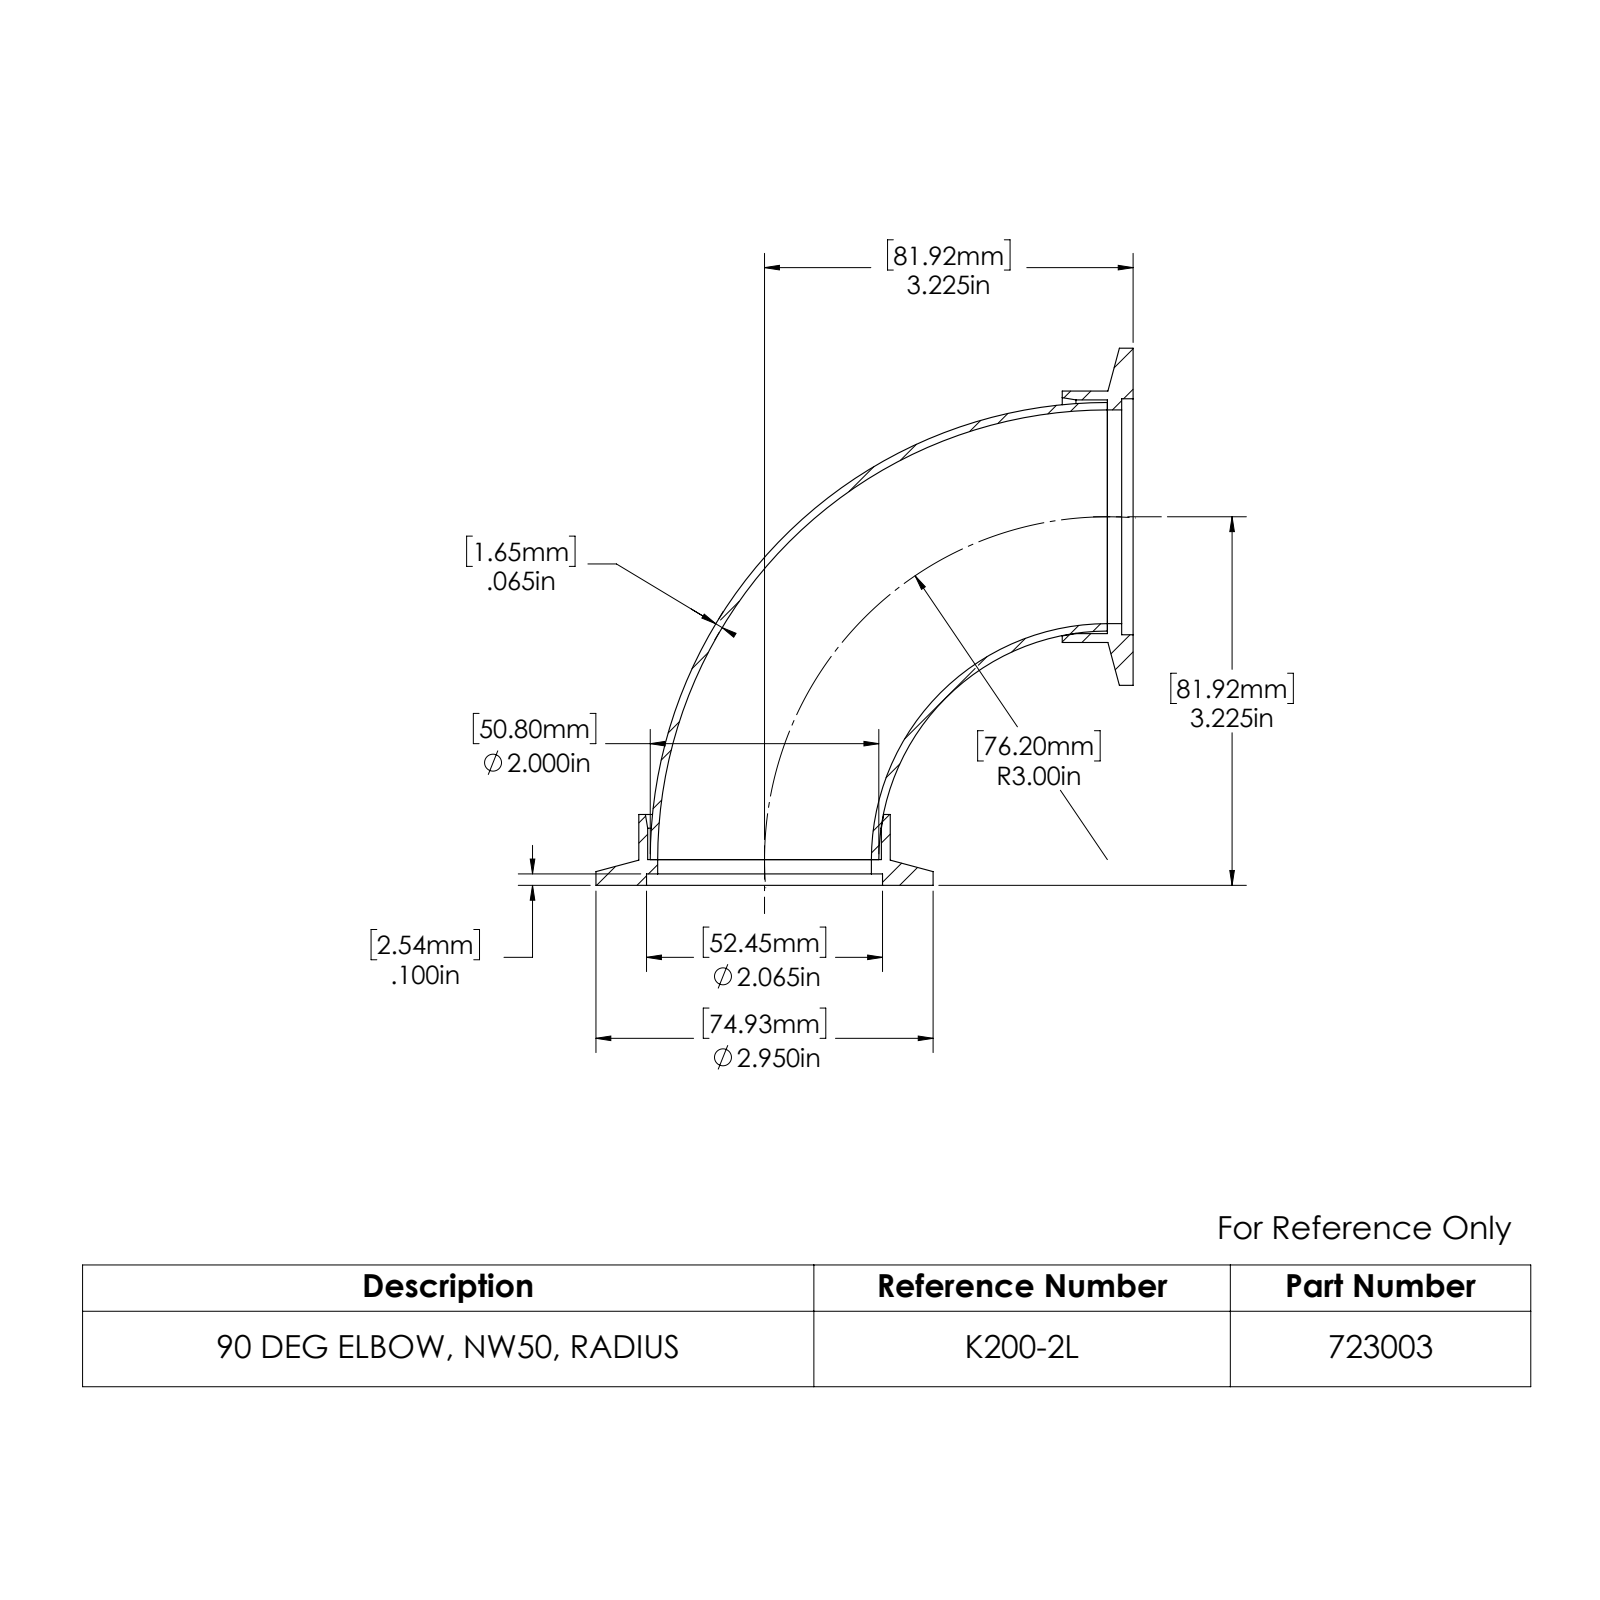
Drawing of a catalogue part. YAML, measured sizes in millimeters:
part_name: "972303; 403503; 723003"
step_written_by: "SolidWorks 2022 (AUTOMOTIVE_DESIGN)"
units: millimeters
bodies: {solids: 3, faces: 38, planar: 10, cylindrical: 20, other: 8}
overall_size: [119.4, 119.4, 74.9]
volume: 59700
surface_area: 58220
round_holes:
  - {diameter: 47.5, count: 2}
  - {diameter: 51.9, count: 2}
  - {diameter: 52.5, count: 2}
round_bosses_or_shafts:
  - {diameter: 74.9, count: 2}
  - {diameter: 55.9, count: 2}
face_to_face_distances: [5.7, 3.2, 2.5, 10, 13.2, 15.7]
